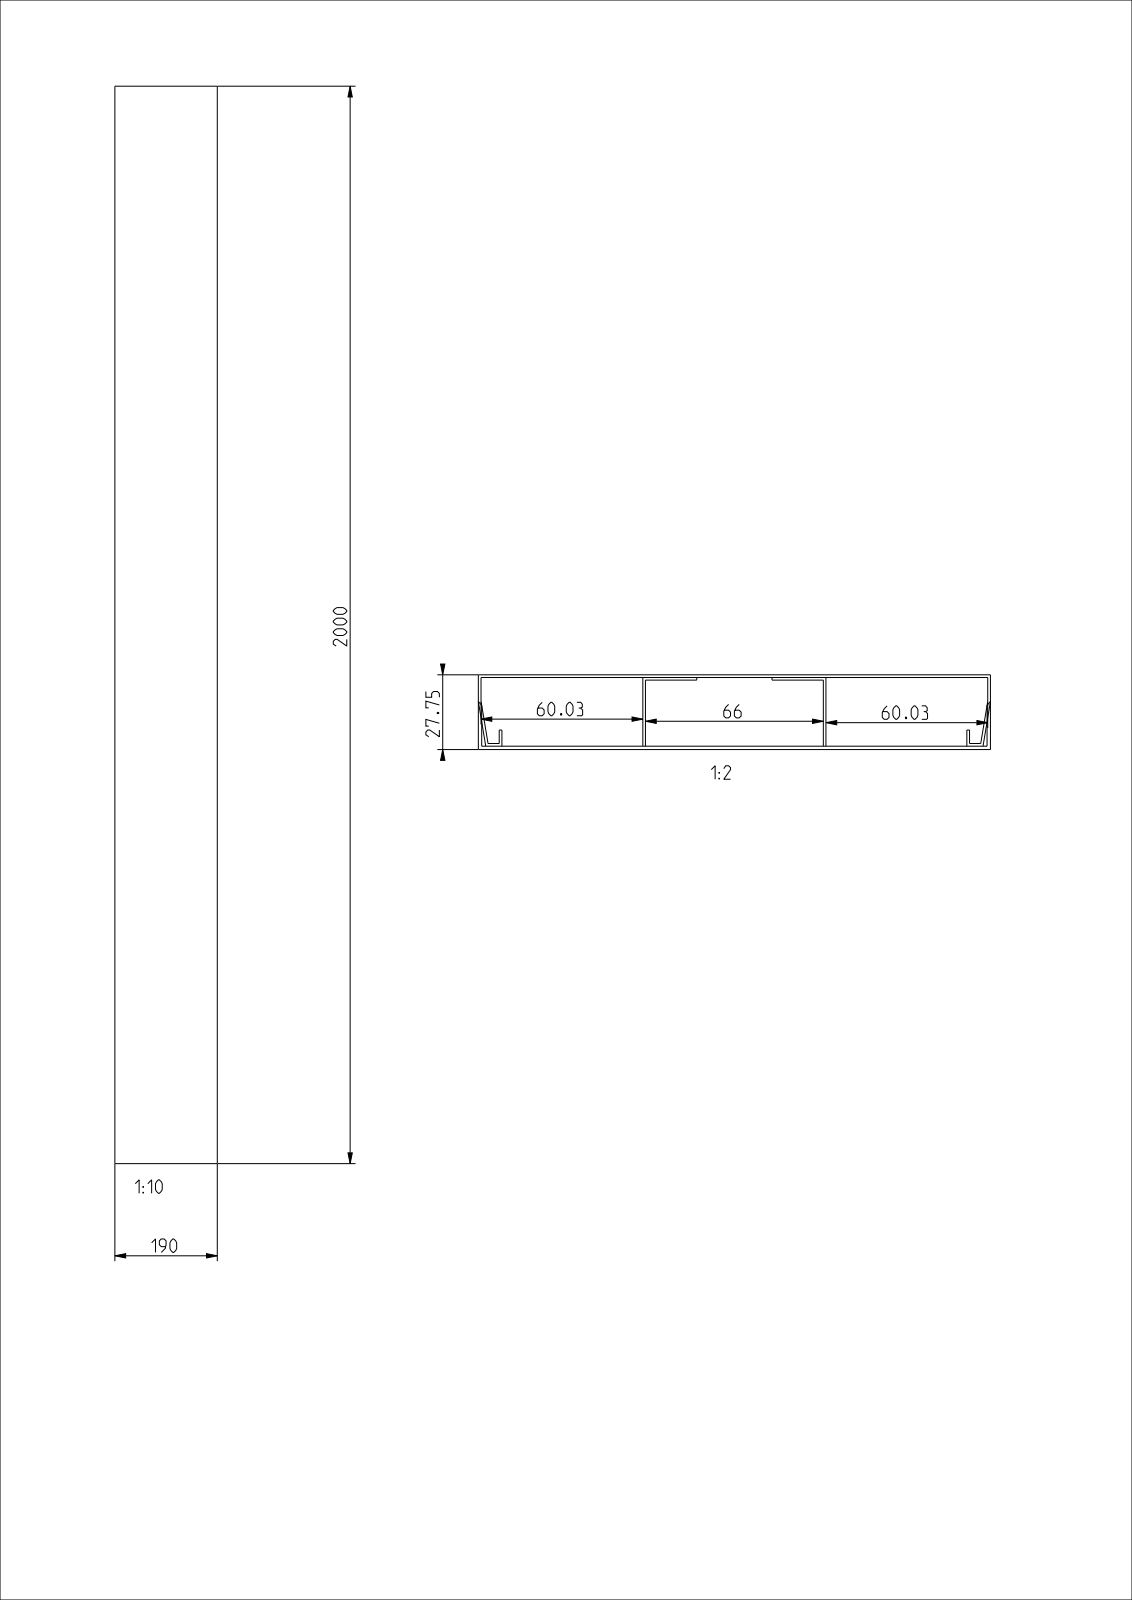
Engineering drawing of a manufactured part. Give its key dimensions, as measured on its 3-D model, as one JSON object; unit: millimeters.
{"part_name": "UK190283KUN_UNTERTEIL; UK190283KUN_OBERTEIL; UK190283KUN_ASM", "step_written_by": "CREO PARAMETRIC BY PTC INC, 2022024 (AUTOMOTIVE_DESIGN)", "units": "millimeters", "bodies": {"solids": 2, "faces": 46, "planar": 46, "cylindrical": 0, "other": 0}, "overall_size": [2000, 190, 27.75], "volume_mm3": 1249000, "surface_area_mm2": 2150000, "face_to_face_distances": [1.25, 26.5, 27.75, 1, 25.5, 26.75, 0.97, 61.03, 128.97, 62]}
